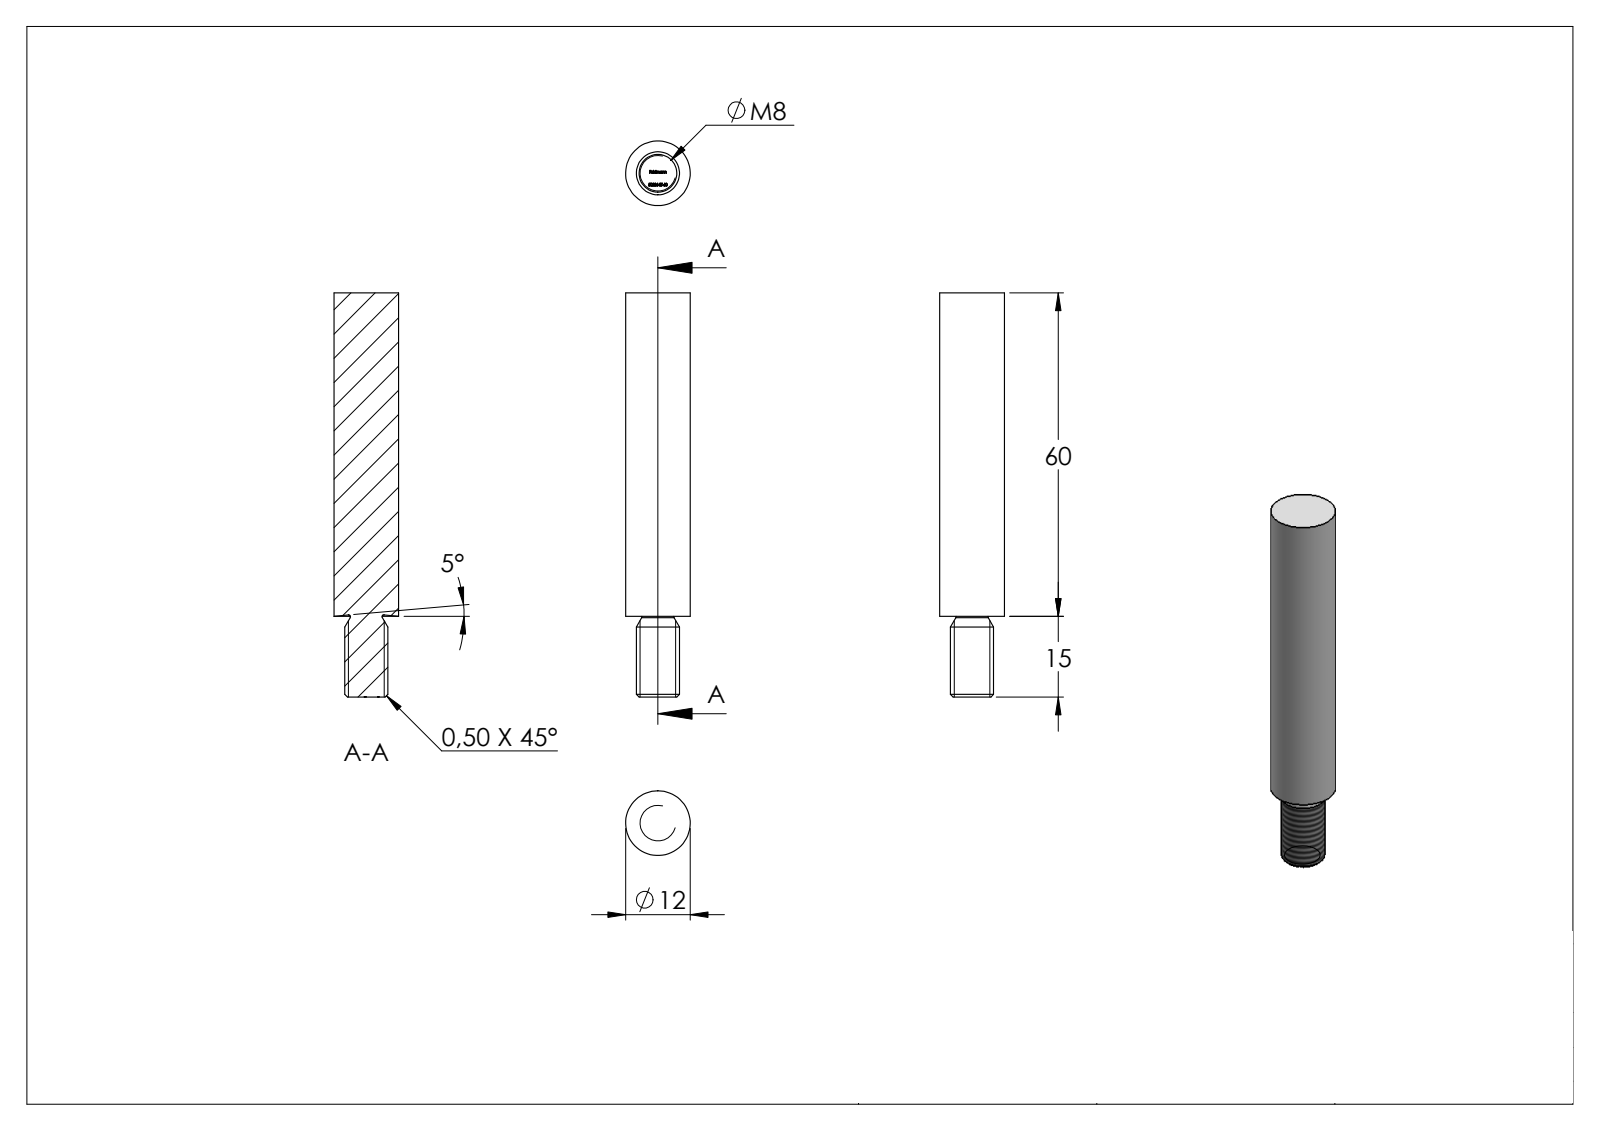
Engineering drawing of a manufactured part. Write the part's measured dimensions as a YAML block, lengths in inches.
part_name: "50236-ST-60"
step_written_by: "SolidWorks 2015 (CONFIG_CONTROL_DESIGN)"
units: inches
bodies: {solids: 1, faces: 262, planar: 121, cylindrical: 4, other: 137}
overall_size: [2.953, 0.472, 0.472]
volume: 0.458
surface_area: 4.472
round_bosses_or_shafts:
  - {diameter: 0.472, count: 1}
  - {diameter: 0.315, count: 1}
face_to_face_distances: [2.953, 2.949, 0.043, 0.094, 0.021, 0.018, 0.094, 0.022, 0.041, 0.019]
